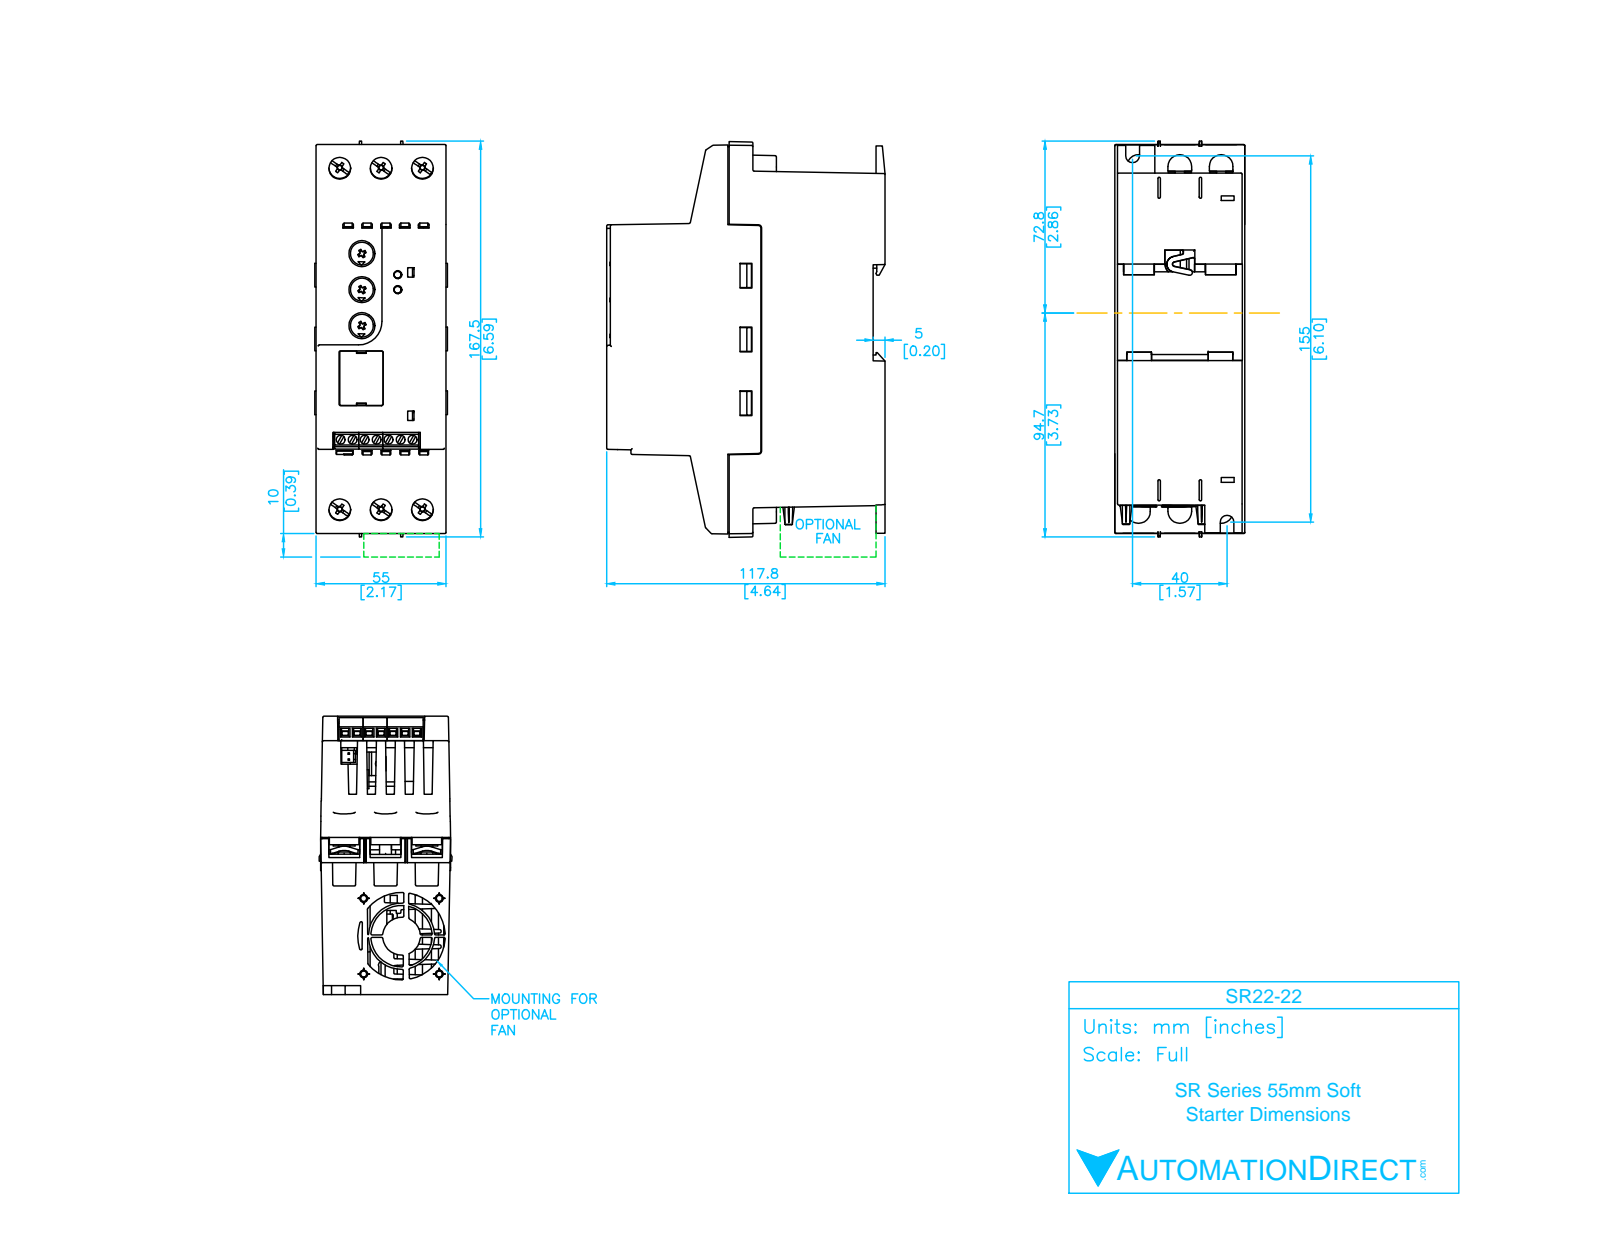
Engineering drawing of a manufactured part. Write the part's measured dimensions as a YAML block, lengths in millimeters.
part_name: "SR22-22"
step_written_by: "SolidWorks 2013 (AUTOMOTIVE_DESIGN)"
units: millimeters
bodies: {solids: 1, faces: 623, planar: 483, cylindrical: 110, other: 30}
overall_size: [164.5, 117.8, 55.87]
volume: 813460
surface_area: 69575
round_holes:
  - {diameter: 3.5, count: 7}
  - {diameter: 9.5, count: 6}
  - {diameter: 11.3, count: 3}
  - {diameter: 4, count: 2}
  - {diameter: 27.66, count: 1}
  - {diameter: 40.29, count: 1}
round_bosses_or_shafts:
  - {diameter: 10.44, count: 3}
  - {diameter: 29.09, count: 1}
  - {diameter: 16, count: 1}
partial_cylinders:
  - {radius: 0.5, count: 35}
  - {radius: 4.88, count: 6}
  - {radius: 1, count: 2}
  - {radius: 2.75, count: 2}
  - {radius: 10, count: 1}
face_to_face_distances: [54.97, 54.94, 55, 117.8, 5.14, 112.66, 141.5, 18, 0.5, 1.5]
hole_center_spacings: [5.25, 10.5, 15.75, 18, 137.19, 21, 136, 15]
